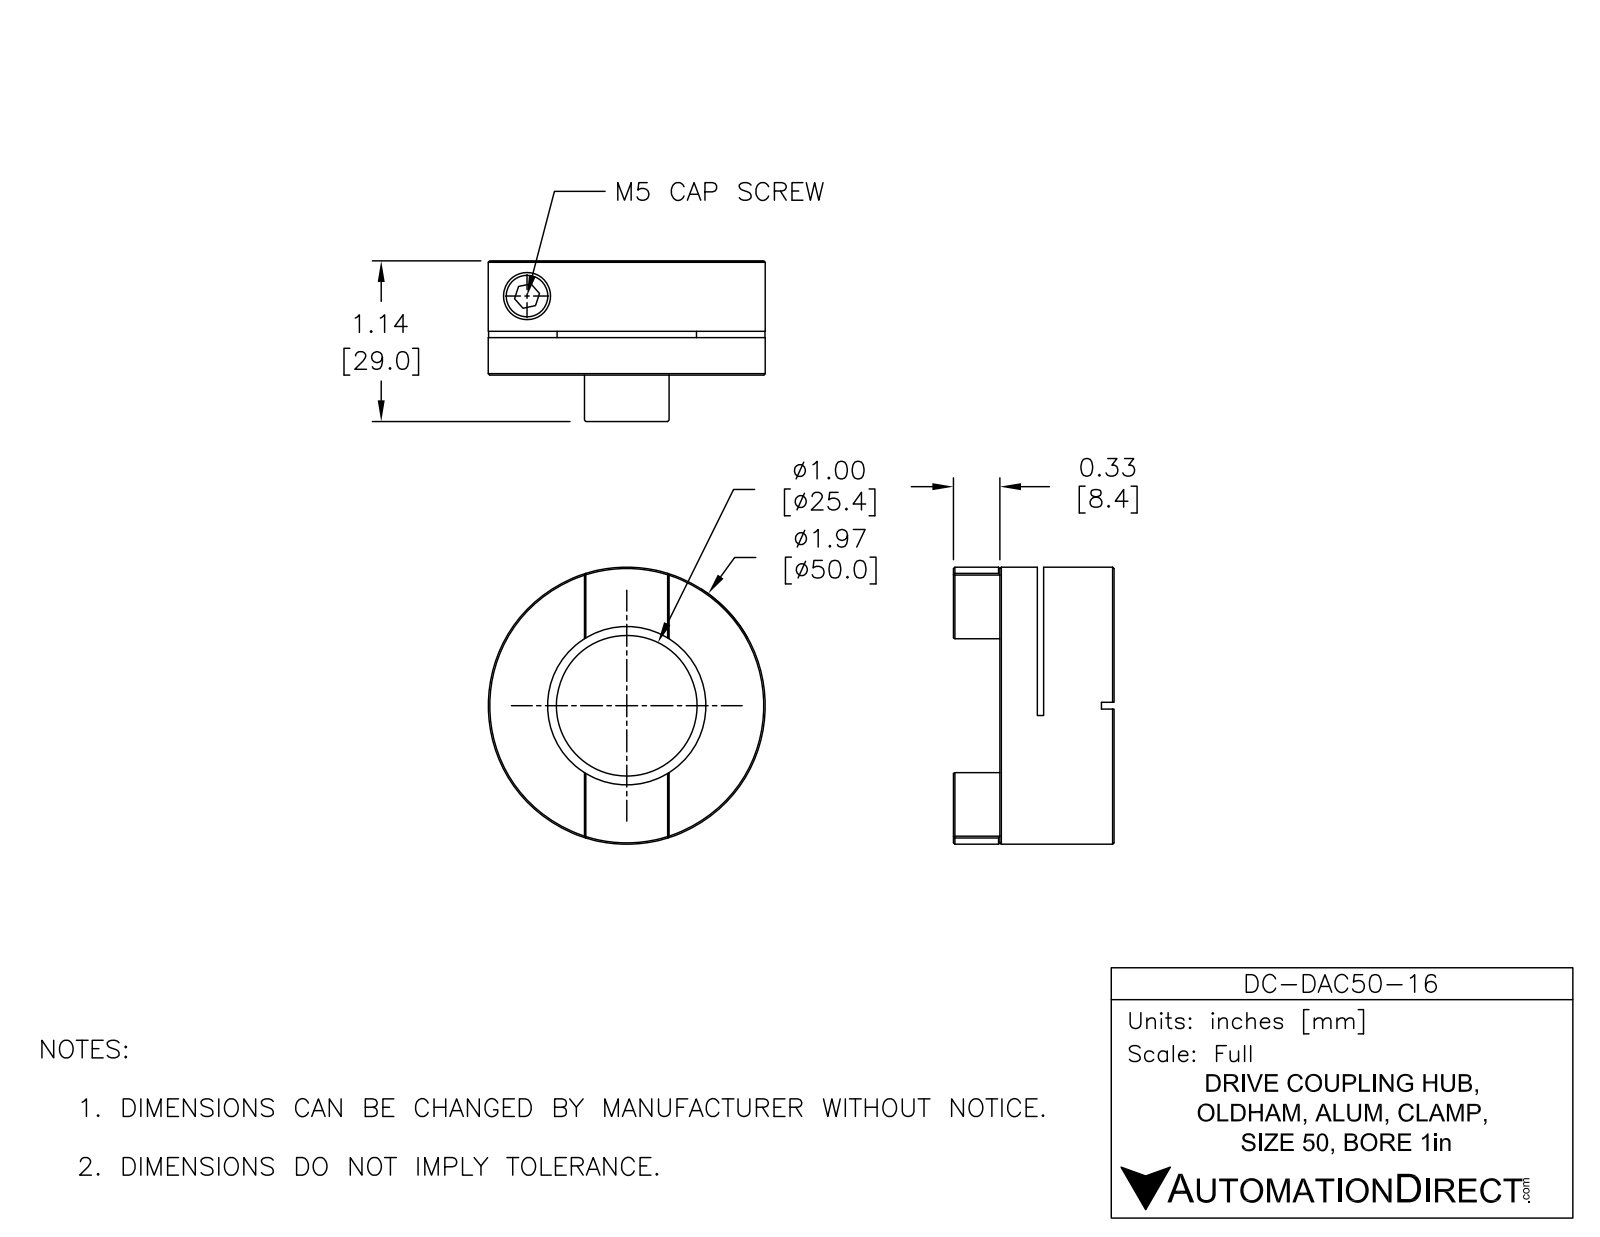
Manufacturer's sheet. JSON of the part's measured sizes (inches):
{"part_name": "DC-DAC50-16", "step_written_by": "SolidWorks 2015 (AUTOMOTIVE_DESIGN)", "units": "inches", "bodies": {"solids": 0, "faces": 57, "planar": 29, "cylindrical": 18, "other": 10}, "overall_size": [1.969, 1.969, 1.141], "round_holes": [[0.163, 1], [0.217, 1], [0.394, 1], [1, 1], [1.125, 1]], "round_bosses_or_shafts": [[1.969, 1]], "partial_cylinders_radius": [[1, 1]], "face_to_face_distances": [0.811, 0.545, 0.266, 0.5, 0.045, 0.311, 1.141, 0.641, 0.596, 0.33]}
